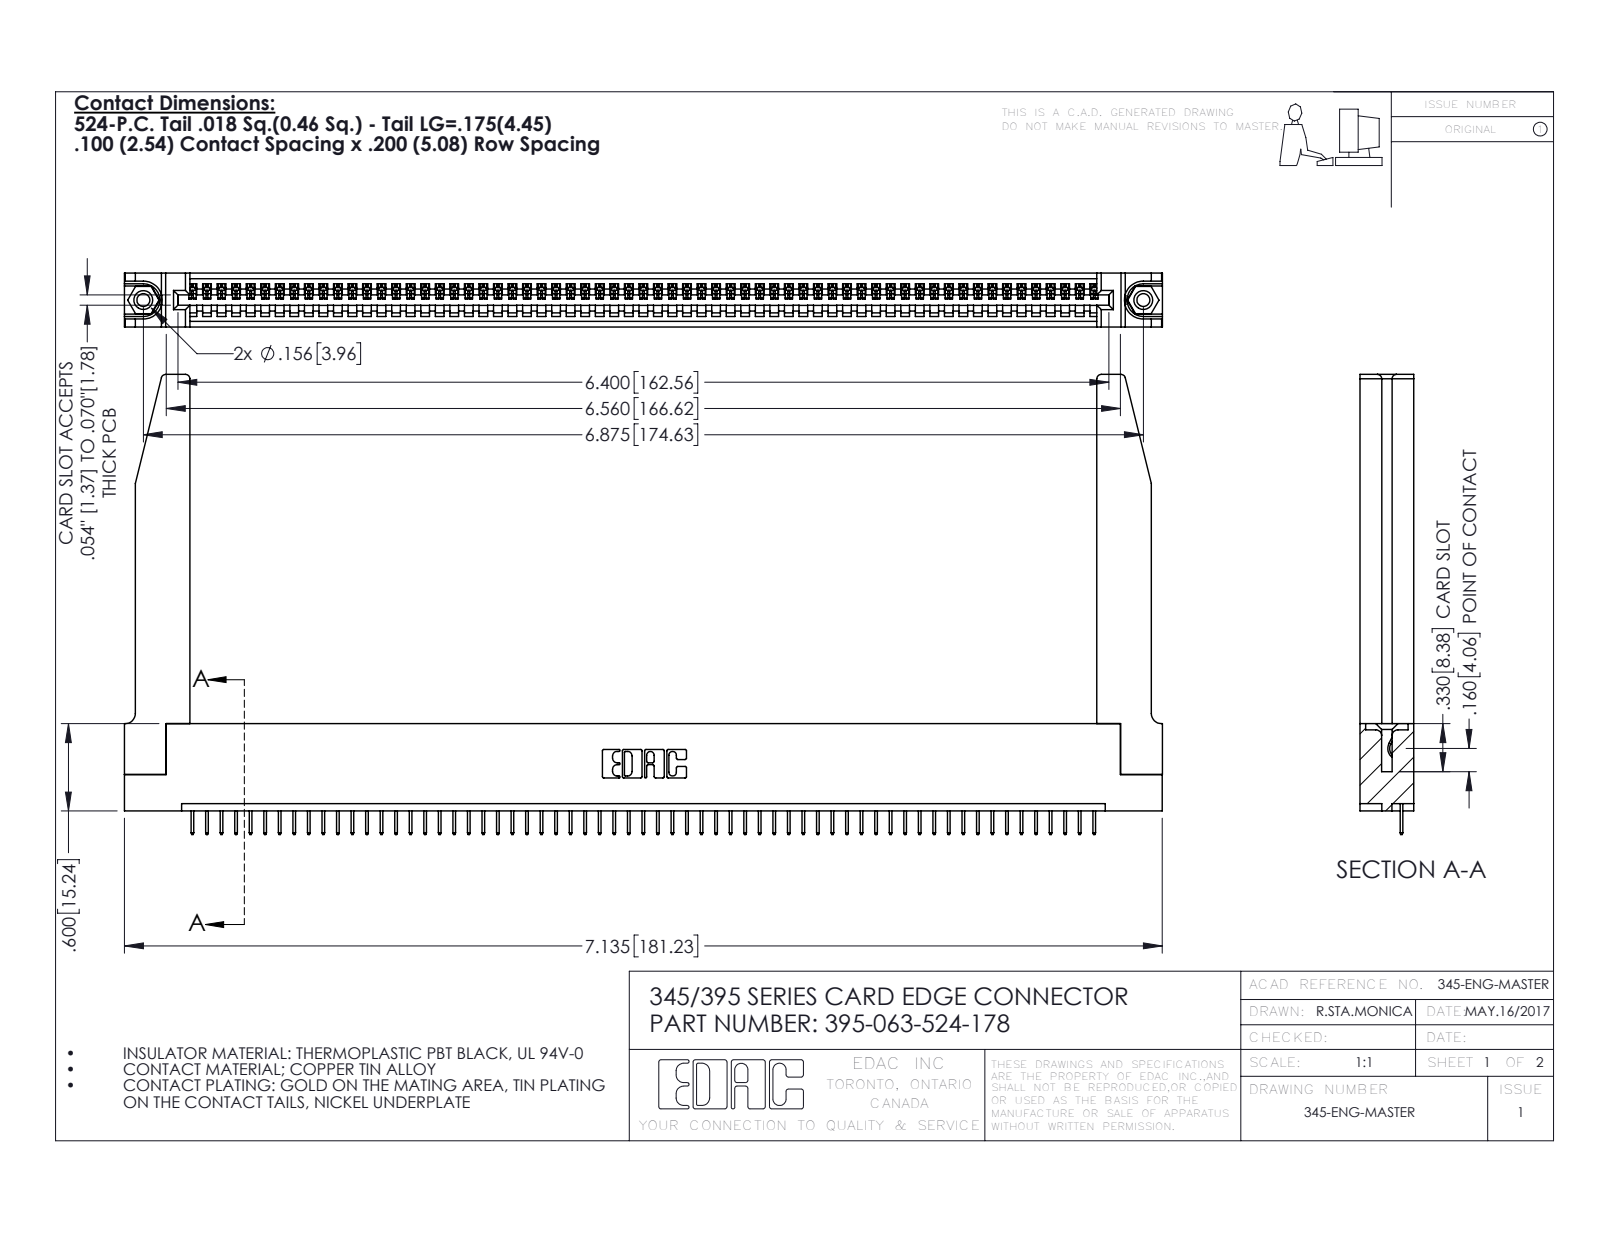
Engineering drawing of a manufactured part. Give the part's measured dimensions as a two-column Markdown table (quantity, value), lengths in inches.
| quantity | value |
| --- | --- |
| part name | 395-063-524-178; 345 Part_Flush Mounting Lugs - 0.156 Dia-TH; 345-250-001_345-250-001-102; 345-220-078_345-220-078 (+1 more) |
| STEP written by | SolidWorks 2016 (CONFIG_CONTROL_DESIGN) |
| units | inches |
| bodies | 68 solids, 4266 faces (3120 planar, 1094 cylindrical, 52 other) |
| overall size | 7.136 × 3.162 × 0.37 |
| volume | 1.52 in³ |
| surface area | 45.12 in² |
| round holes (diameter × count) | 0.089 × 2, 0.125 × 2, 0.156 × 2, 0.064 × 1 |
| round bosses / shafts (diameter × count) | 0.155 × 2 |
| partial cylindrical surfaces (radius × count) | 0.006 × 126, 0.01 × 22, 0.03 × 8, 0.007 × 6, 0.031 × 6, 0.026 × 3, 0.031 × 2, 0.04 × 2 |
| main face-to-face distances | 0.37, 0.072, 0.298, 0.2, 0.098, 0.272, 0.025, 0.225, 0.072, 0.148 |
| hole center spacings | 0.27, 6.639, 6.875 |
